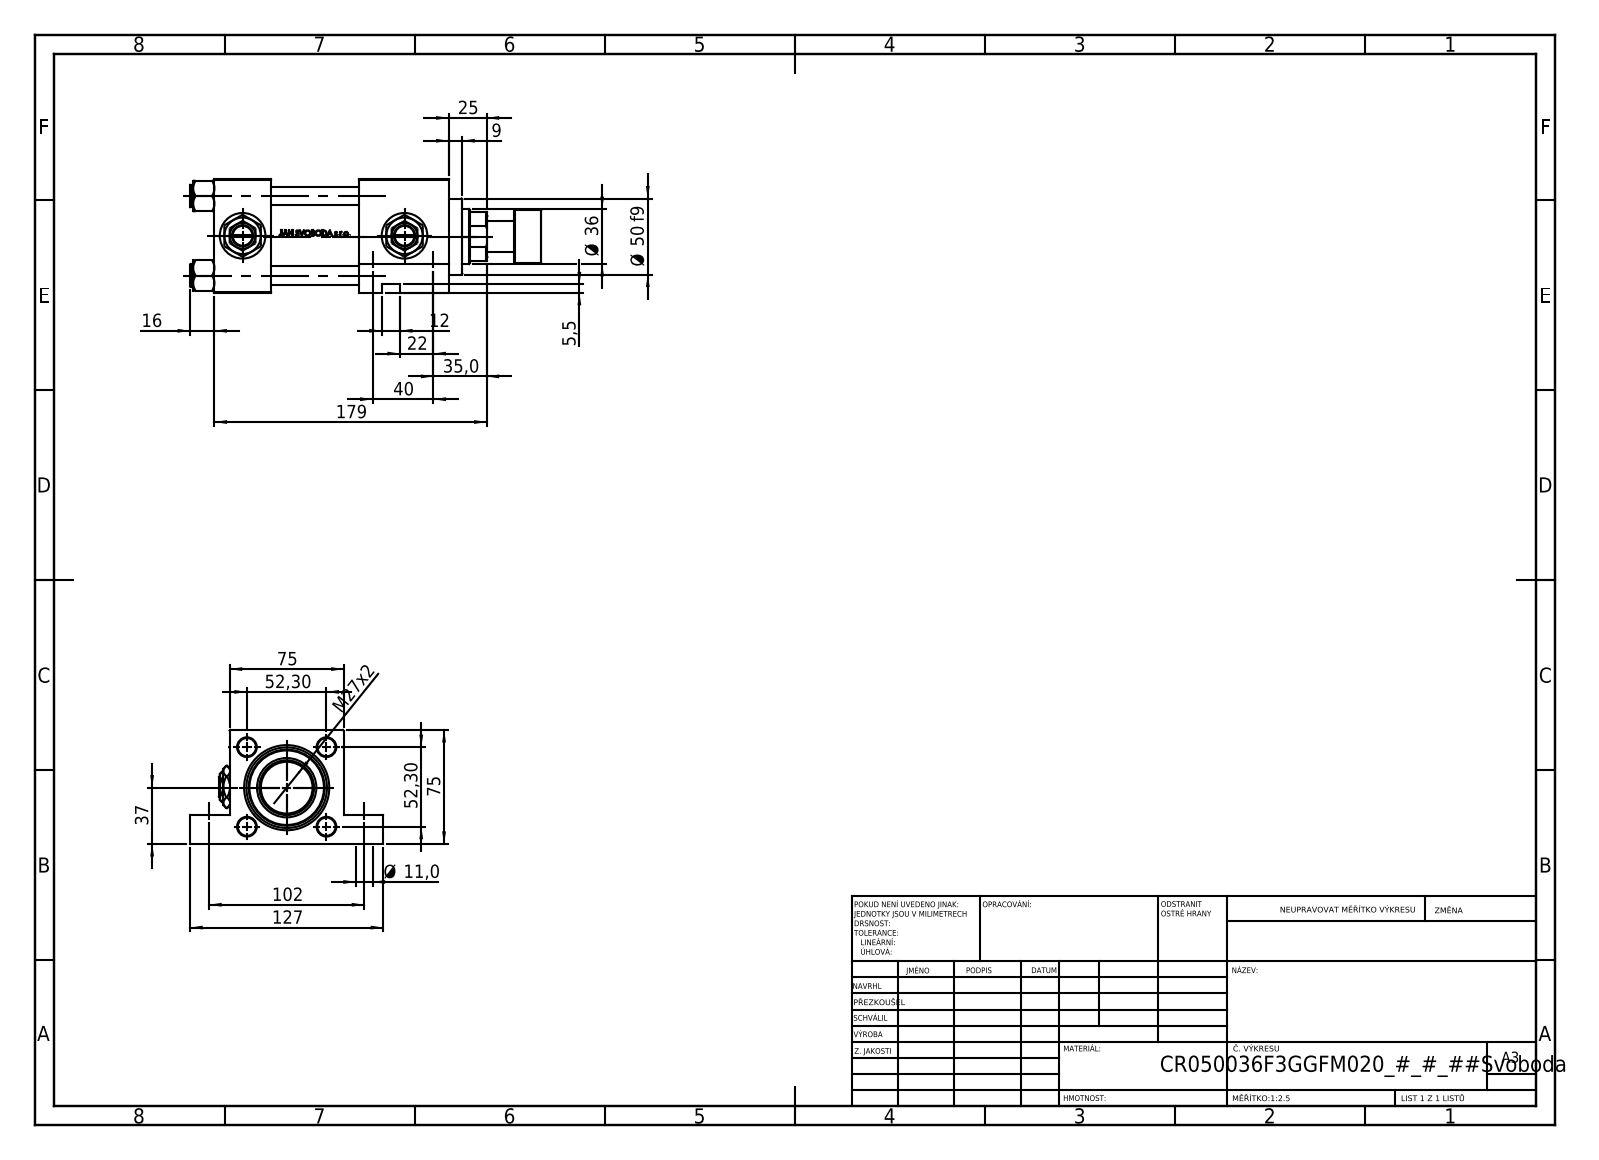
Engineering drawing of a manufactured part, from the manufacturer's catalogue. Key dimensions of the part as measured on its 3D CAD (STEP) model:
Part name (STEP PRODUCT): V215CR_VCP_F; V215CR_F_TYCINKA; V215_VC_A; V215CR_ROD_END_F (+3 more)
STEP written by: SolidWorks 2019 (CONFIG_CONTROL_DESIGN)
Units: millimetres
Bodies: 14 solids, 1216 faces (488 planar, 140 cylindrical, 588 other)
Overall size (bounding box): 231 × 127 × 75
Volume: 753 549 mm³ · Surface area: 174 540 mm²
Round holes (diameter × count): ⌀12 ×4, ⌀20.96 ×4, ⌀30 ×4, ⌀7 ×3, ⌀11 ×2, ⌀11 ×2, ⌀25.5 ×1, ⌀36 ×1, ⌀39 ×1, ⌀41 ×1, ⌀53 ×1
Round bosses / shafts (diameter × count): ⌀15 ×4, ⌀56 ×1, ⌀50 ×1, ⌀35 ×1, ⌀21 ×1
Main face-to-face distances: 75, 37, 58, 95, 59, 154, 117, 19, 56, 74.8
Hole centre spacings: 52.3, 36.63, 37.34, 40, 51.62, 60.21, 73.96, 99.56
